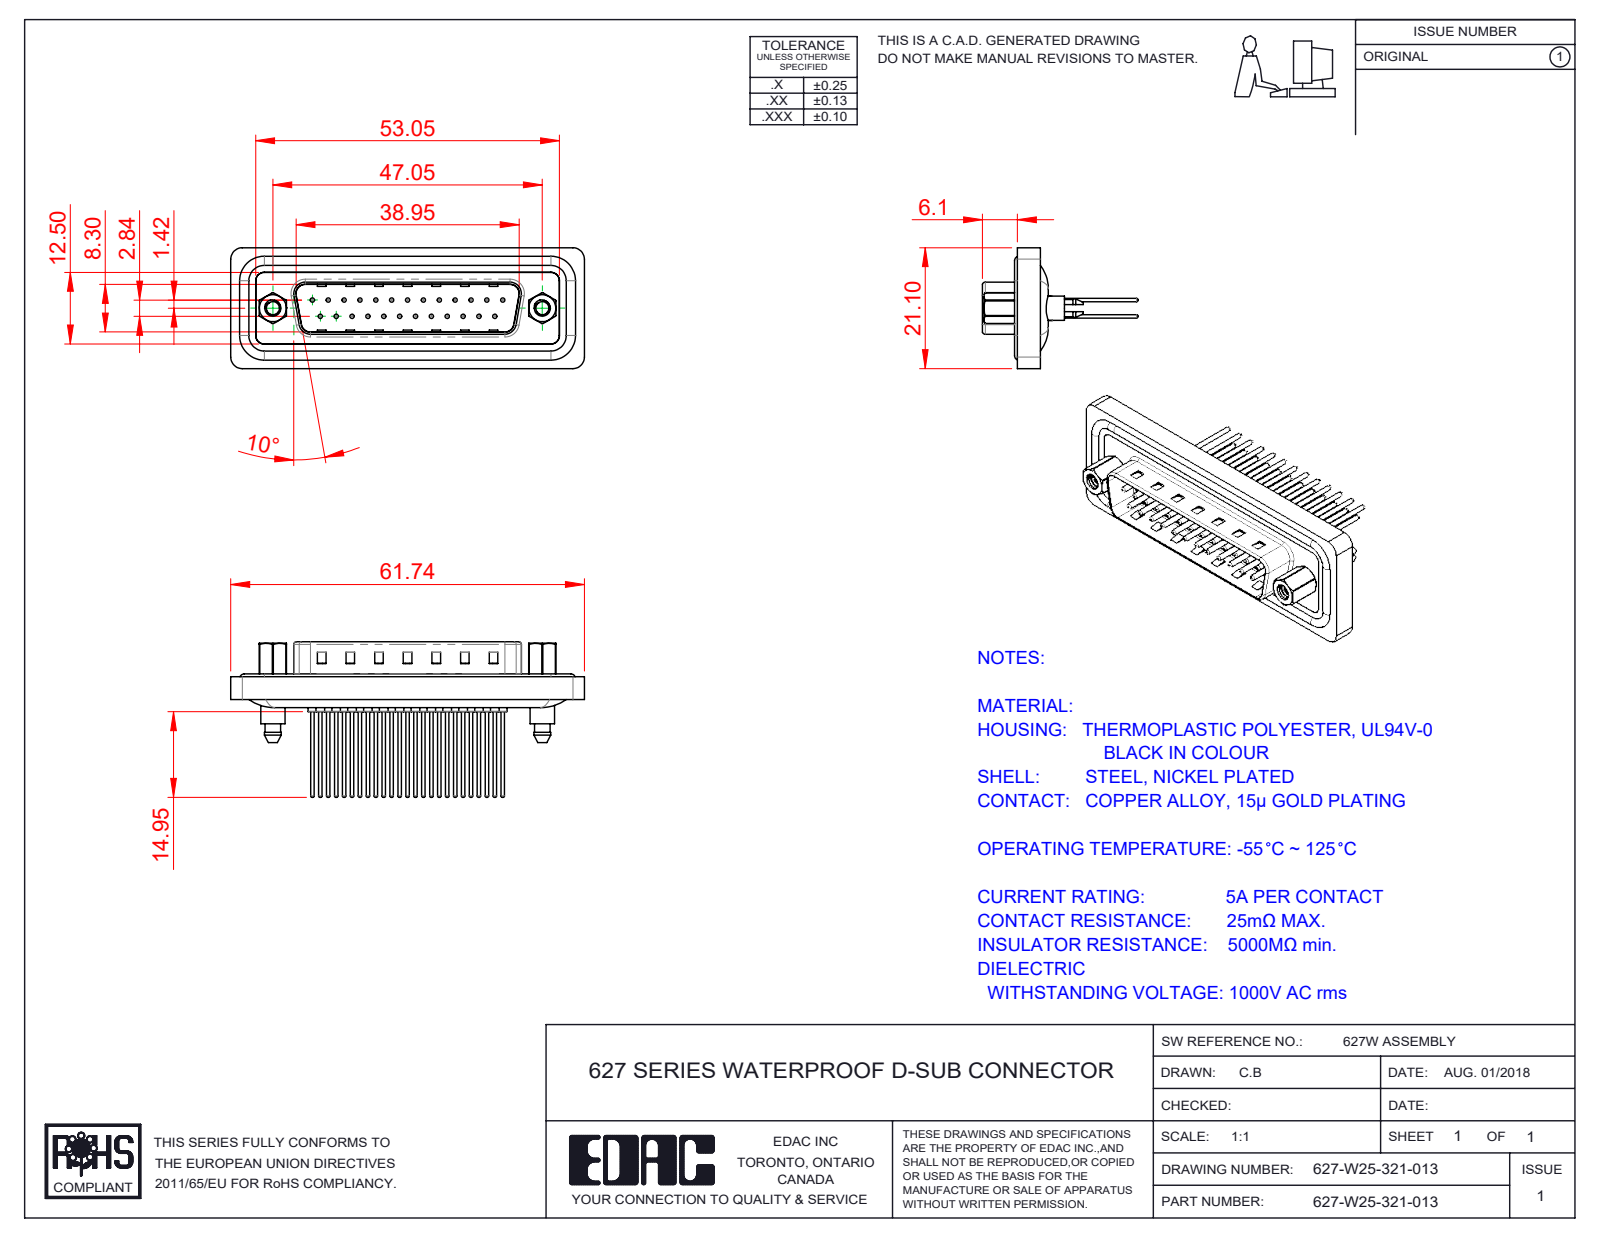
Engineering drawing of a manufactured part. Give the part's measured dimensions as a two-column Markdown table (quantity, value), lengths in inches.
| quantity | value |
| --- | --- |
| part name | 627W 4-40 Hex Standoff; 627W Shell Front_25 Contacts; 627W Contact Row 1_21; 627W Contact Row 2_21 (+4 more) |
| STEP written by | SolidWorks 2020 (CONFIG_CONTROL_DESIGN) |
| units | inches |
| bodies | 33 solids, 1541 faces (394 planar, 648 cylindrical, 499 other) |
| overall size | 2.431 × 1.069 × 0.831 |
| volume | 0.393 in³ |
| surface area | 17.59 in² |
| round holes (diameter × count) | 0.03 × 25, 0.059 × 25, 0.063 × 25, 0.079 × 25, 0.089 × 2, 0.09 × 2, 0.157 × 2, 0.167 × 2, 0.189 × 2 |
| round bosses / shafts (diameter × count) | 0.024 × 25, 0.059 × 8, 0.063 × 4, 0.213 × 2, 0.193 × 2, 0.11 × 2, 0.167 × 1 |
| partial cylindrical surfaces (radius × count) | 0.059 × 14, 0.079 × 12, 0.02 × 8, 0.063 × 6, 0.035 × 4, 0.106 × 4, 0.169 × 4, 0.016 × 2 |
| main face-to-face distances | 0.016, 0.063, 0.098, 0.043, 0.114, 0.222, 0.161, 0.177, 0.608, 0.03 |
| hole center spacings | 0.124, 0.218, 0.109, 0.436, 0.198, 0.327, 0.545, 0.198 |
